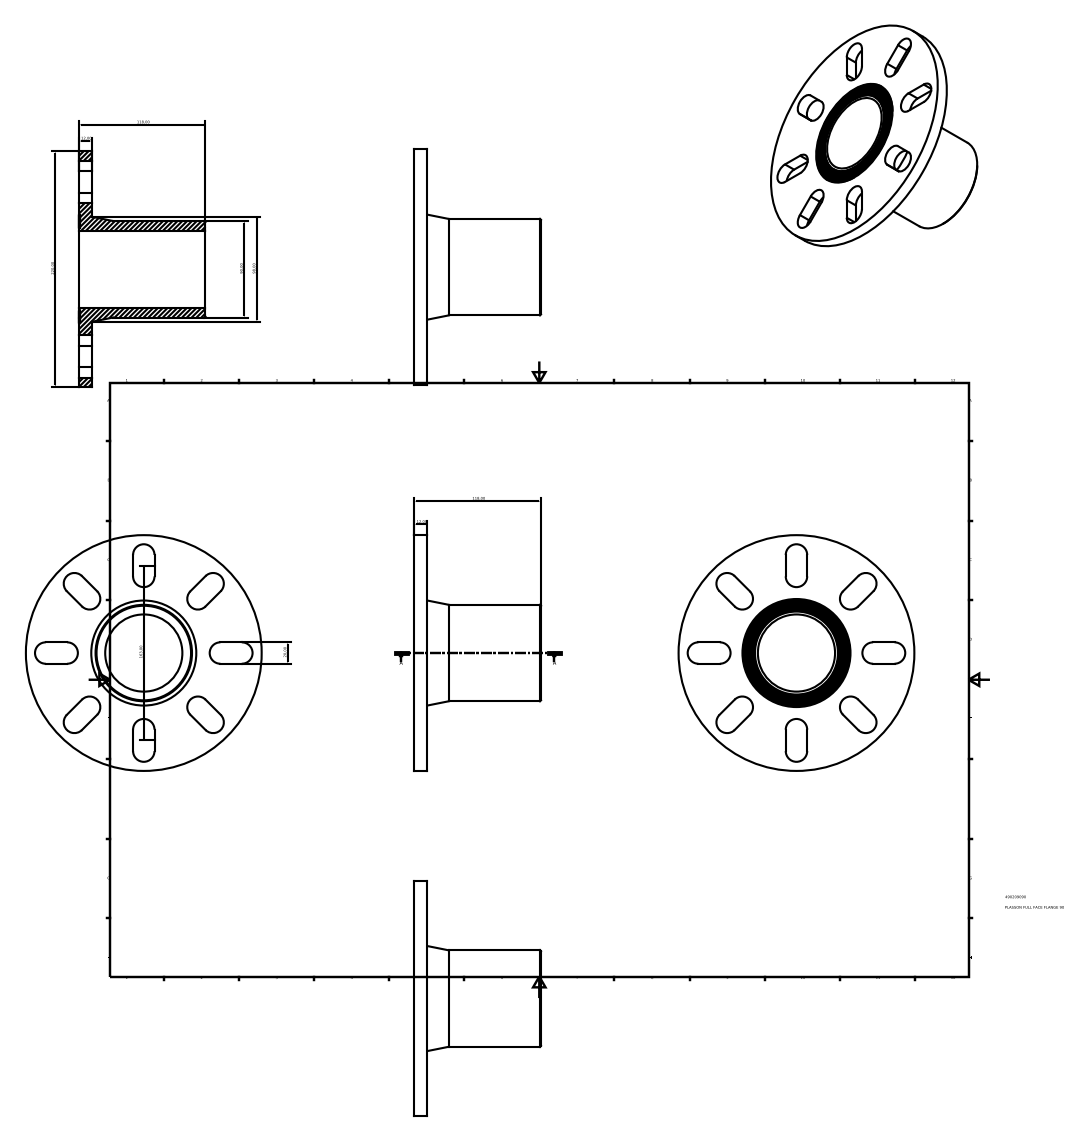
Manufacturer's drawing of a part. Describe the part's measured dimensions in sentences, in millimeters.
The part is named "490209090". Its 3-D file was written by "Autodesk Inventor 2015 (AUTOMOTIVE_DESIGN)". It is 1 solid with 68 faces: 33 planar, 33 cylindrical and 2 other. Overall it measures 220 by 220 by 118 millimeters. Its volume is 591 449 cubic millimeters and its surface area 133 848 square millimeters. Round holes: 1 of diameter 72, 1 of diameter 79.2, 1 of diameter 82.8, 1 of diameter 86.4, 1 of diameter 90, 1 of diameter 93.6, 1 of diameter 97.2, 1 of diameter 100.8. Round bosses or shafts: 1 of diameter 220, 1 of diameter 99, 1 of diameter 95.4, 1 of diameter 91.8, 1 of diameter 88.2, 1 of diameter 84.6, 1 of diameter 81, 1 of diameter 77.4. Partial cylindrical surfaces (rounded edges, fillets, slot ends): 16 of radius 10. The main face-to-face distances are 12, 118, 106, 20, 0.9, 11.1, 117.1.
